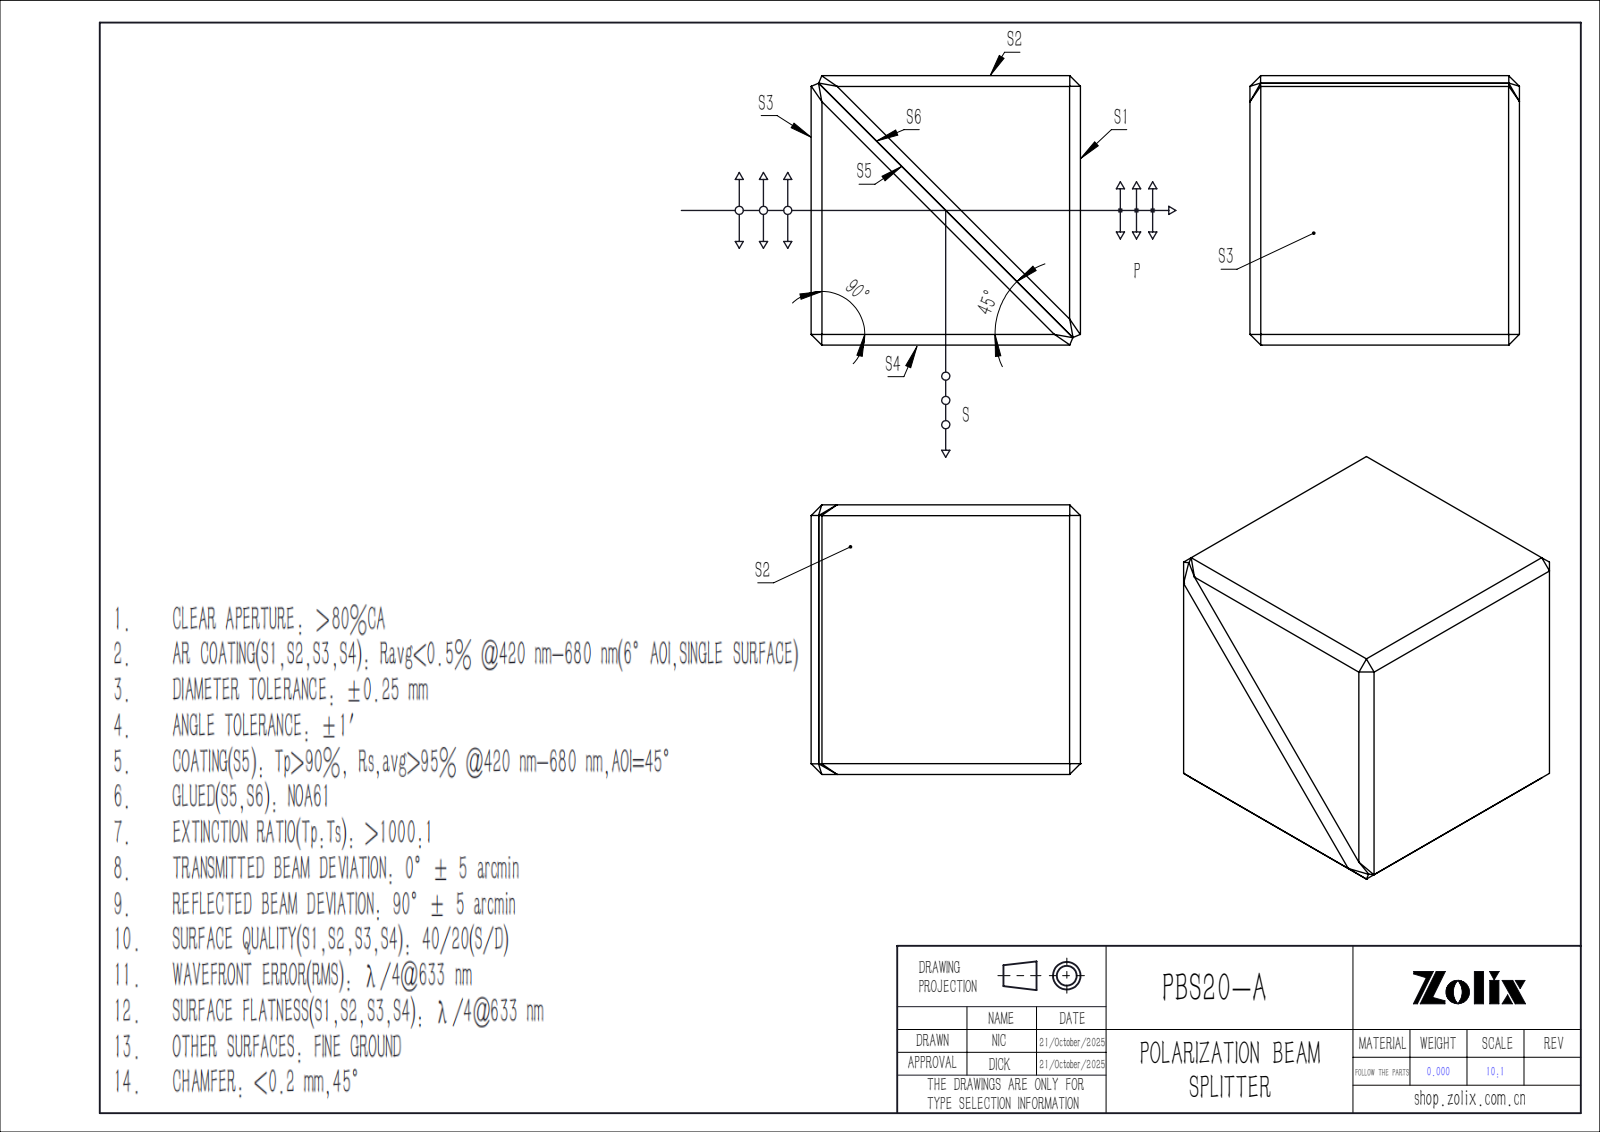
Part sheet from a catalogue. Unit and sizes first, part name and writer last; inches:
Units: inches
Overall size (bounding box): 0.787 × 0.787 × 0.787
Round holes (diameter × count): ⌀0.016 ×1
Main face-to-face distances: 0.787, 1.102, 0.546, 1.015, 0.551, 1.102, 0.551, 0.031, 0.756, 1.178
Volume: 0.488 in³ · Surface area: 5.388 in²
Bodies: 2 solids, 43 faces (41 planar, 2 cylindrical, 0 other)
Part name (STEP PRODUCT): PBS631-1-2; PBS631-1-1; PBS631
STEP written by: SolidWorks 2022 (CONFIG_CONTROL_DESIGN)
